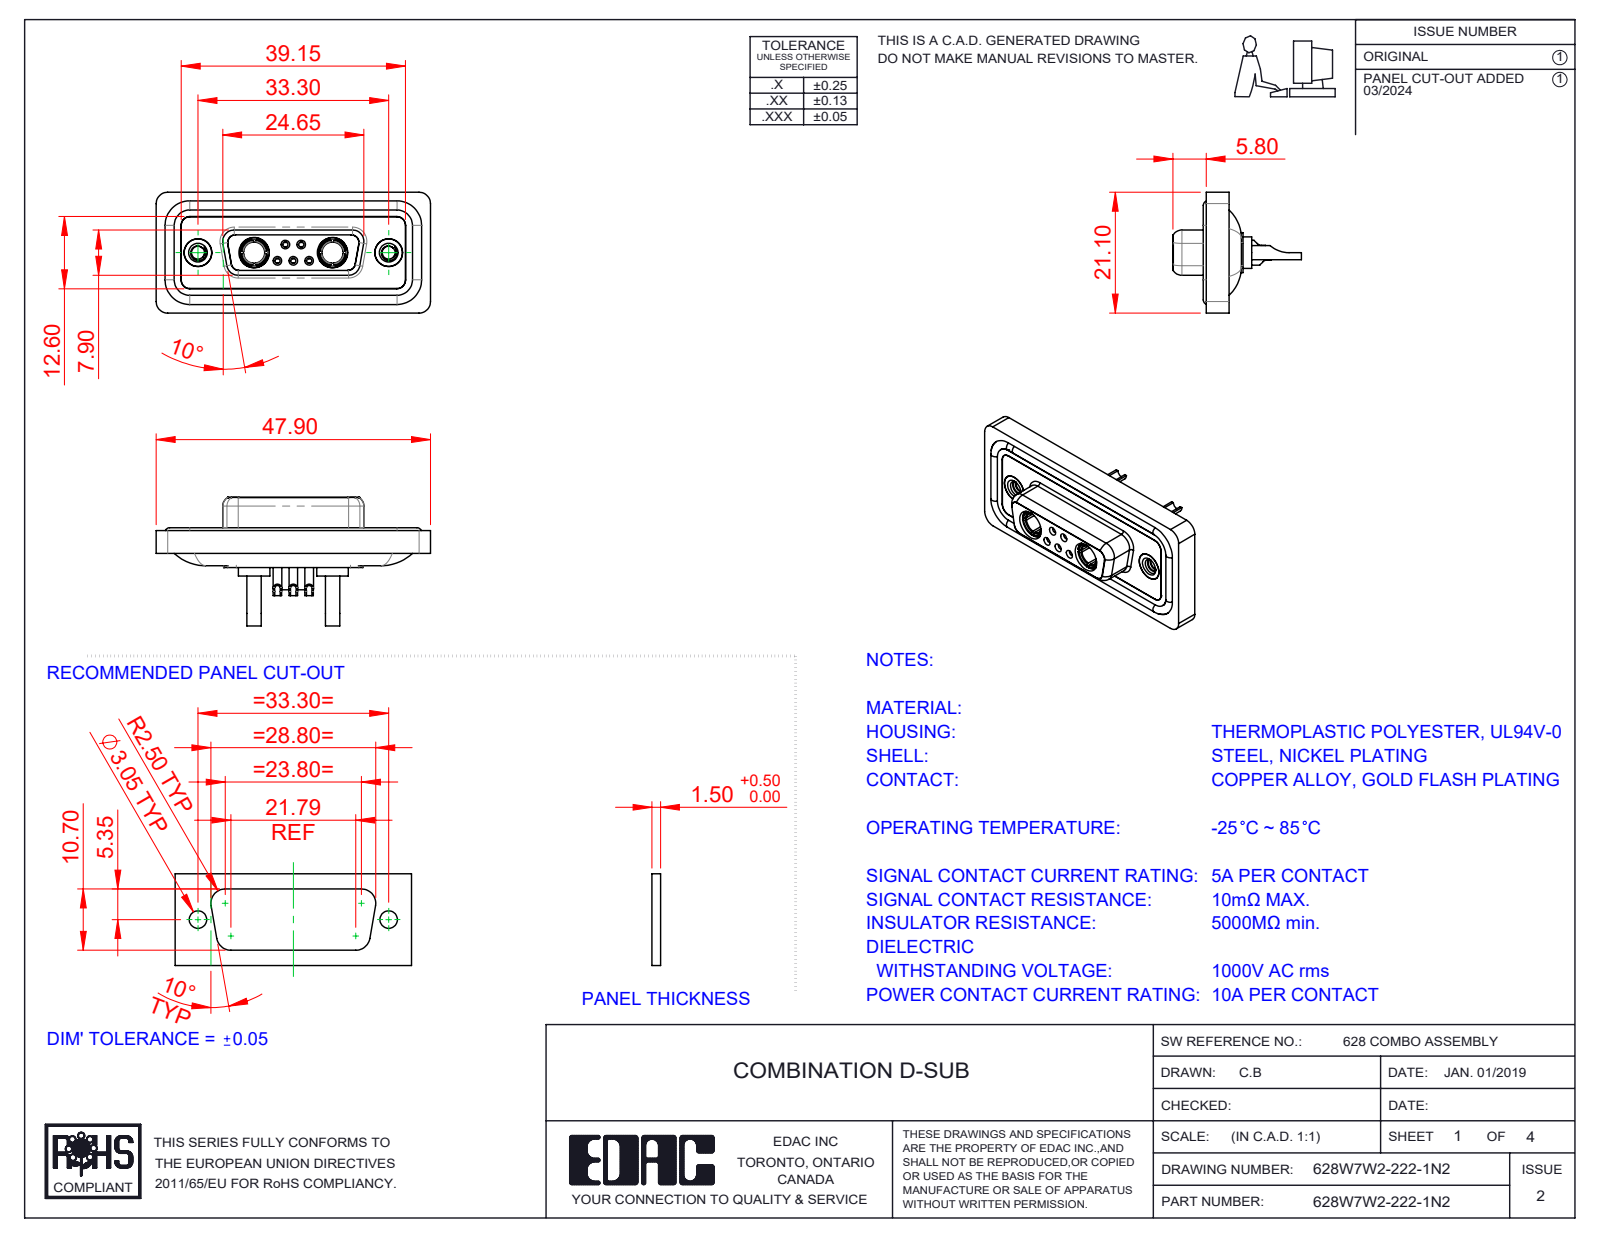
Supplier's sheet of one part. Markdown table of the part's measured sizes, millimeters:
| quantity | value |
| --- | --- |
| part name | 628Combo Waterproof Housing_15 Contacts; 628W7W2-222-1N2; 628Combo Shell Rear_15 Contacts; 628Combo Shell Front_15 Contacts (+5 more) |
| STEP written by | SolidWorks 2023 (CONFIG_CONTROL_DESIGN) |
| units | millimeters |
| bodies | 16 solids, 819 faces (252 planar, 345 cylindrical, 222 other) |
| overall size | 47.9 × 22.45 × 21.1 |
| volume | 6 082 mm³ |
| surface area | 10 035 mm² |
| round holes (diameter × count) | 0.9 × 5, 1 × 5, 1.1 × 5, 1.5 × 5, 2 × 5, 4.85 × 4, 1.6 × 3, 1.7 × 2, 1.7 × 2, 2.26 × 2, 3.7 × 2, 4 × 2 |
| round bosses / shafts (diameter × count) | 1.6 × 6, 2.2 × 5, 5.5 × 2, 5.2 × 2, 4.96 × 2, 4.95 × 2, 4.8 × 2, 4.75 × 2 |
| partial cylindrical surfaces (radius × count) | 1.5 × 22, 2 × 20, 1.35 × 12, 1.6 × 8, 1 × 6, 0.25 × 4, 0.5 × 4, 0.6 × 4 |
| main face-to-face distances | 0.4, 1.8, 1.6, 0.5, 2.9, 1.1, 7.45, 5.65, 6.6, 7.05 |
| hole center spacings | 3.16, 2.77, 9.8, 23.5, 4.31, 4.33, 5.03, 5.04 |
